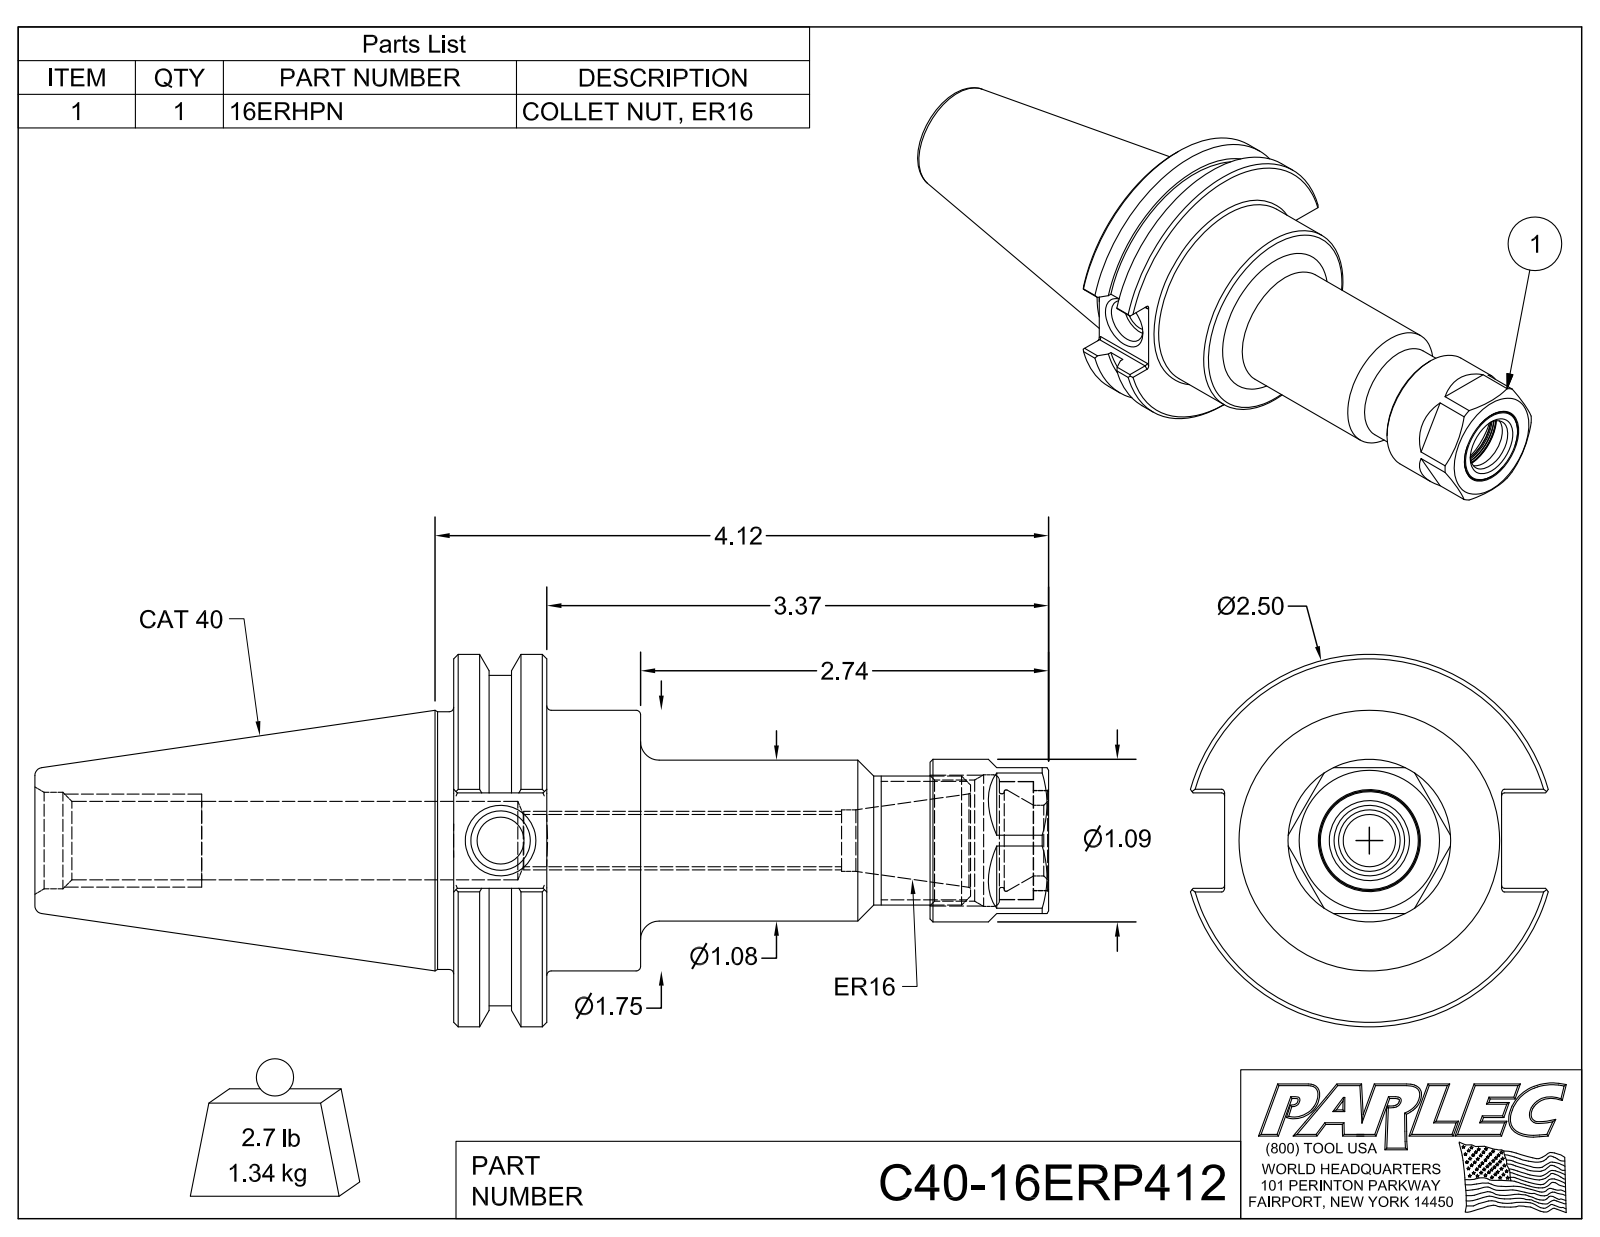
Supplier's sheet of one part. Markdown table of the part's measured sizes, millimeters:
| quantity | value |
| --- | --- |
| part name | C40-16ER4-1; 16ERHPN; C40-16ERP412 |
| STEP written by | Autodesk Inventor 2016 (AUTOMOTIVE_DESIGN) |
| units | millimeters |
| bodies | 3 solids, 130 faces (53 planar, 39 cylindrical, 38 other) |
| overall size | 172.91 × 63.5 × 61.05 |
| volume | 155 002 mm³ |
| surface area | 33 740 mm² |
| round holes (diameter × count) | 8 × 1, 8.92 × 1, 10.13 × 1, 10.5 × 1, 12.04 × 1, 13.38 × 1, 13.39 × 1, 16 × 1, 16.46 × 1, 17.11 × 1, 17.27 × 1, 20.17 × 1 |
| round bosses / shafts (diameter × count) | 63.5 × 1, 56.36 × 1, 44.45 × 1, 43.94 × 1, 27.74 × 1, 27.43 × 1, 22 × 1, 20.07 × 1 |
| partial cylindrical surfaces (radius × count) | 0.51 × 12 |
| main face-to-face distances | 15.88, 31.88, 16, 24.9, 101.48, 85.6, 69.6, 4.32, 20.58, 81.26 |
